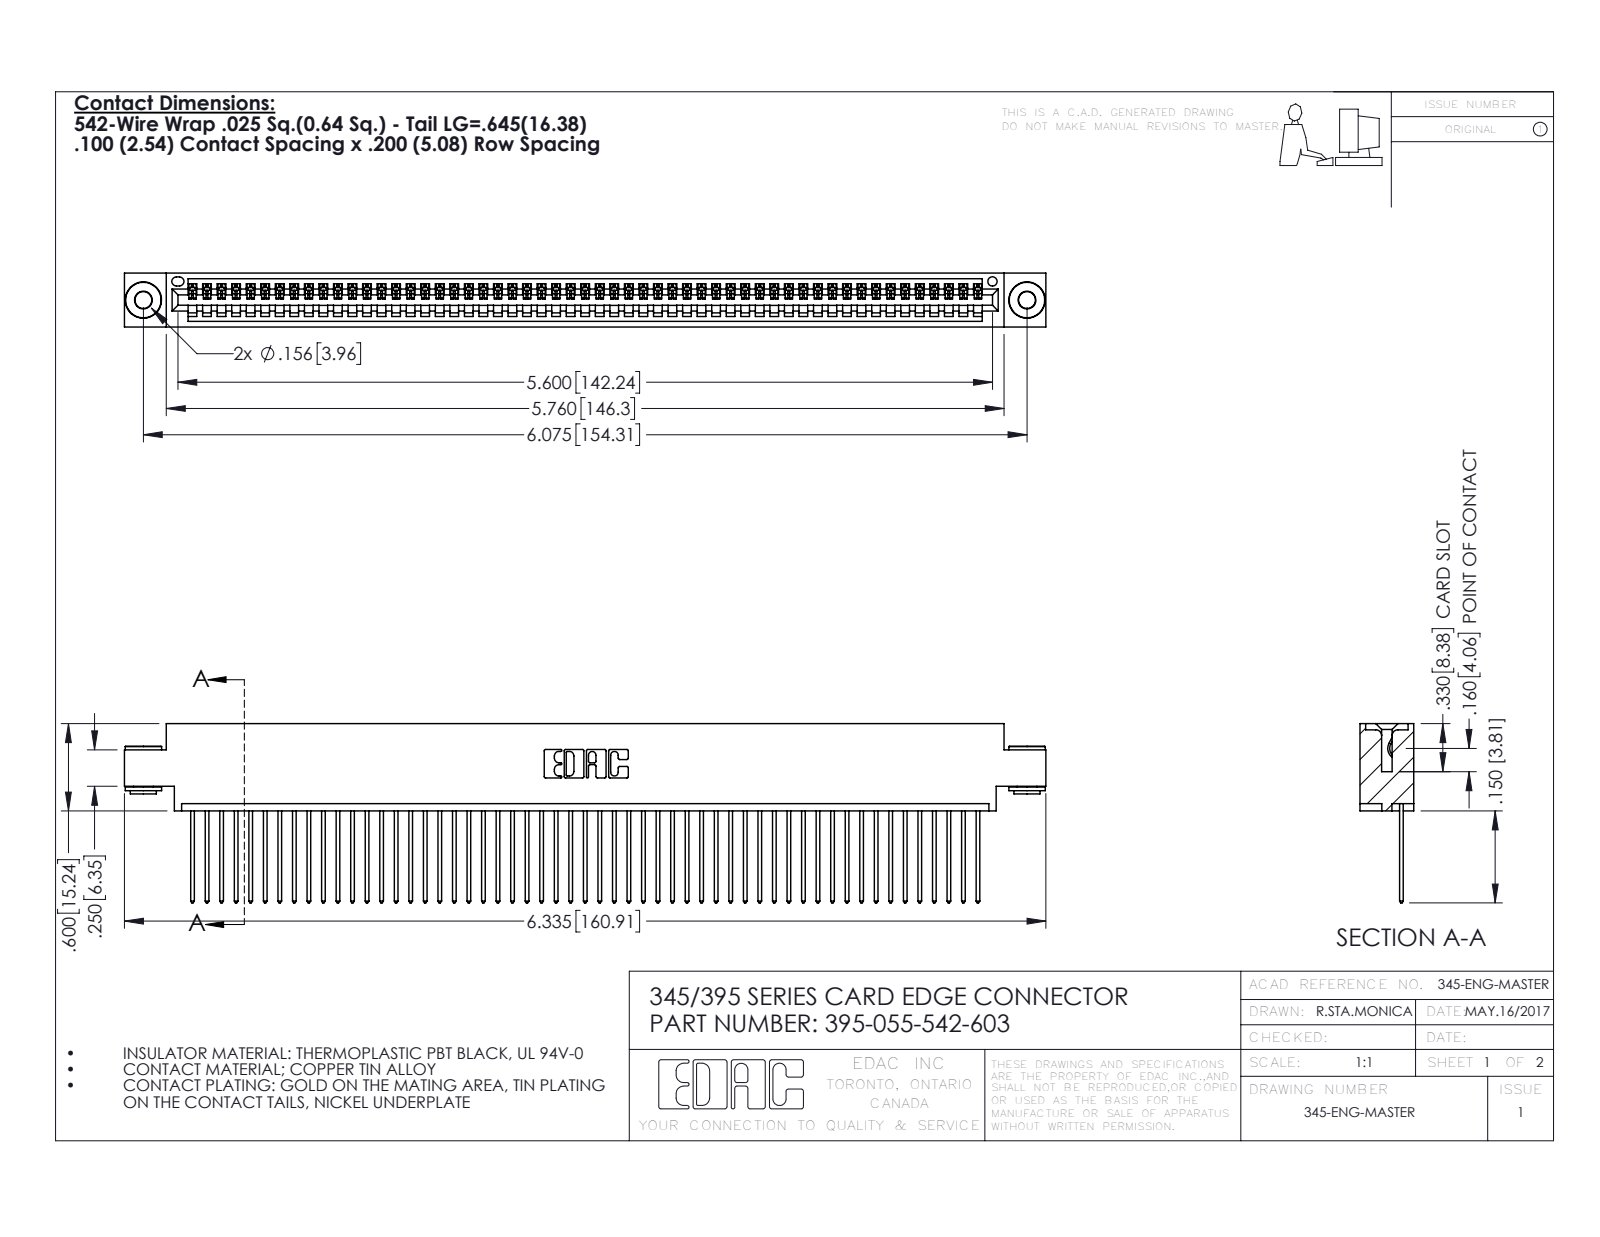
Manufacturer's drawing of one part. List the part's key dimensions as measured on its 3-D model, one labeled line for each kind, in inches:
Part name (STEP PRODUCT): 395-055-542-603; 345-292-001_345-293-142; 345 Part_0.170 Offset - 0.156 Dia-TH; 345-250-002_345-250-002-102
STEP written by: SolidWorks 2016 (CONFIG_CONTROL_DESIGN)
Units: inches
Bodies: 58 solids, 3358 faces (2294 planar, 1056 cylindrical, 8 other)
Overall size (bounding box): 6.335 × 1.232 × 0.37
Volume: 0.941 in³ · Surface area: 33.76 in²
Round holes (diameter × count): ⌀0.116 ×2, ⌀0.156 ×2, ⌀0.064 ×1
Round bosses / shafts (diameter × count): ⌀0.25 ×2, ⌀0.18 ×2, ⌀0.136 ×2
Partial cylindrical surfaces — rounded edges, fillets, slot ends (radius × count): R0.006 ×110, R0.01 ×110, R0.01 ×22, R0.007 ×6, R0.031 ×6, R0.026 ×3, R0.031 ×2, R0.04 ×2
Main face-to-face distances: 0.072, 0.298, 0.37, 0.098, 0.272, 0.025, 0.2, 0.225, 0.175, 0.149
Hole centre spacings: 0.27, 5.839, 6.075
